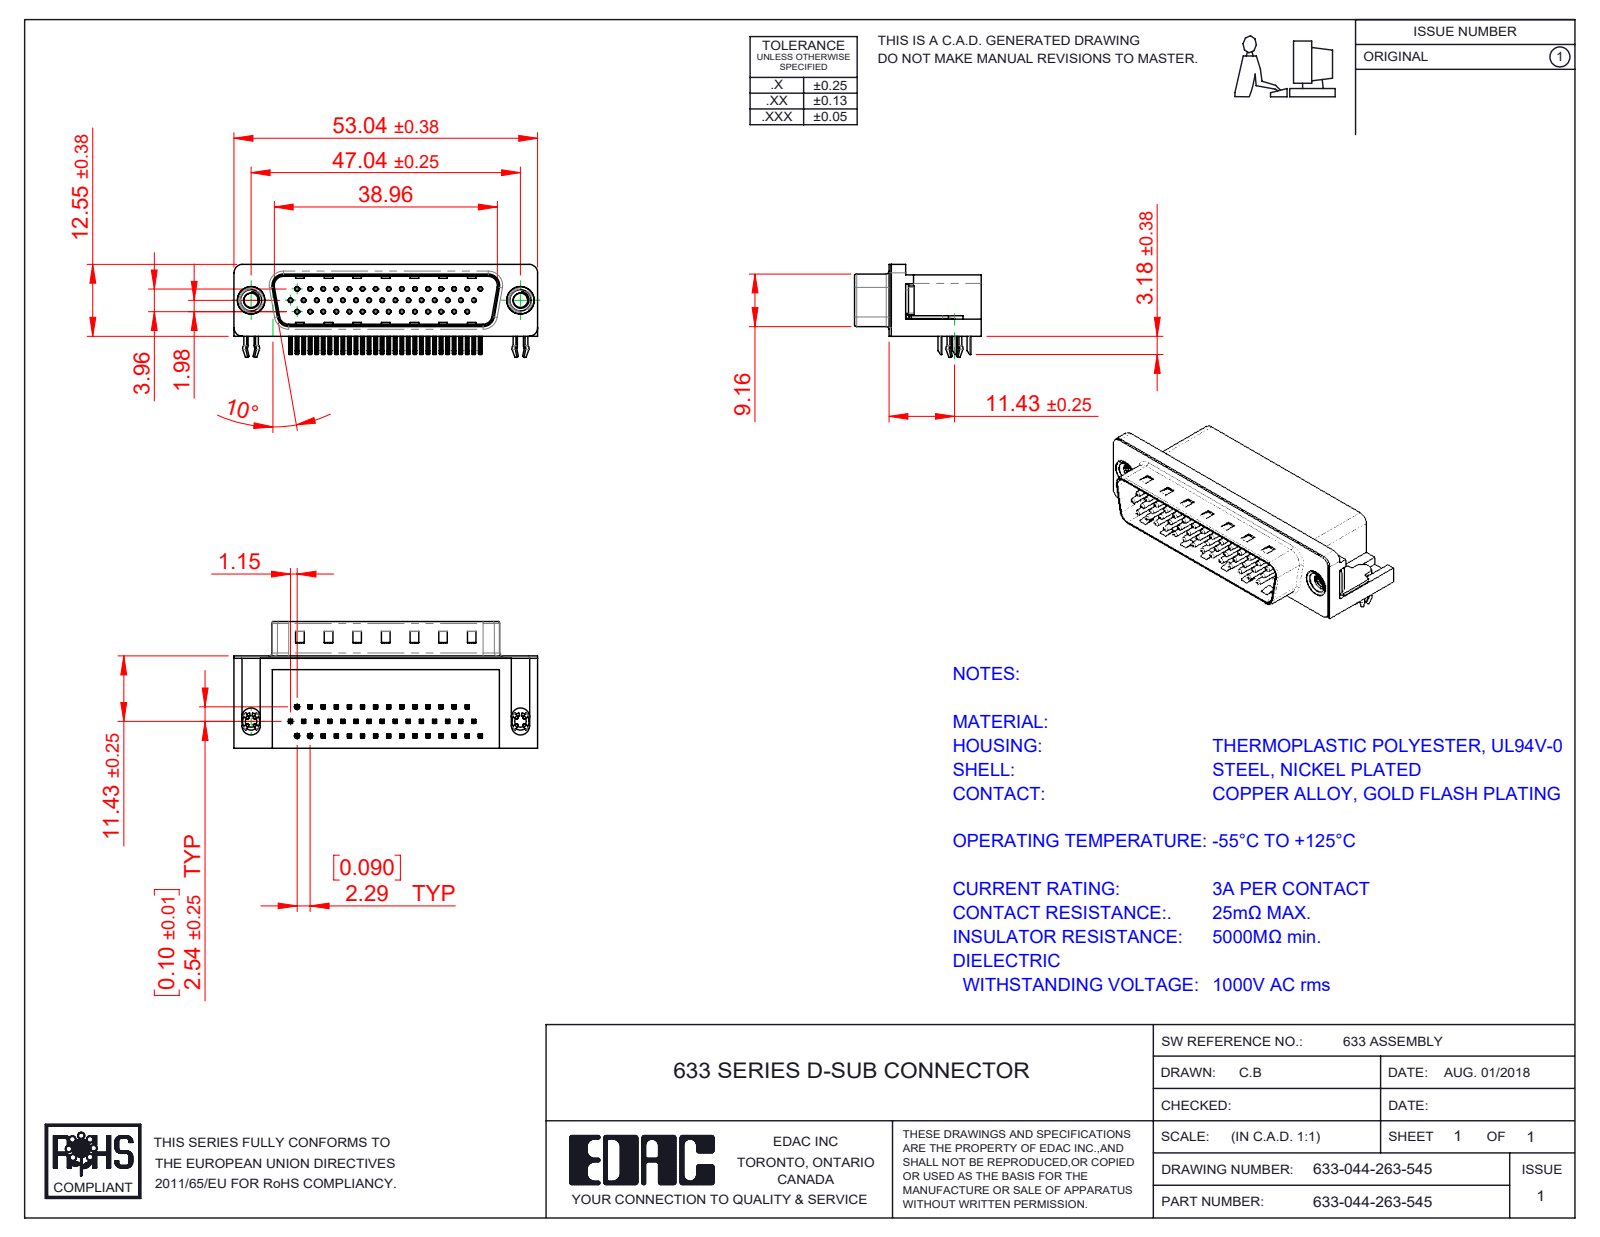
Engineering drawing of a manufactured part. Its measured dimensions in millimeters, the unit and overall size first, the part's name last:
Units: millimetres
Overall size (bounding box): 53.04 × 22.1 × 16.25
Round holes (diameter × count): ⌀0.35 ×44, ⌀0.8 ×44, ⌀2 ×2, ⌀2.5 ×2, ⌀4 ×2, ⌀4.8 ×2, ⌀5 ×2
Round bosses / shafts (diameter × count): ⌀0.75 ×44, ⌀4.9 ×2, ⌀4.75 ×2, ⌀3.9 ×2, ⌀3 ×2
Partial cylindrical surfaces — rounded edges, fillets, slot ends (radius × count): R0.25 ×188, R0.12 ×88, R1 ×16, R0.5 ×9, R1.6 ×8, R1.5 ×7, R0.9 ×4, R2 ×4
Main face-to-face distances: 0.4, 10.35, 15.7, 2.9, 8.76, 2.5, 2.1, 16.1, 10.7, 2.54
Hole centre spacings: 2.29, 4.57, 4.58, 2.28, 6.87, 9.16, 11.45, 2.27
Volume: 8 119 mm³ · Surface area: 10 296 mm²
Bodies: 50 solids, 3810 faces (2359 planar, 1070 cylindrical, 381 other)
Part name (STEP PRODUCT): 633 Contact Middle; 633 Shell_44 Contact; 633 Housing_44 Contact; 633 M3 Threaded Rivet (+4 more)
STEP written by: SolidWorks 2016 (CONFIG_CONTROL_DESIGN)
